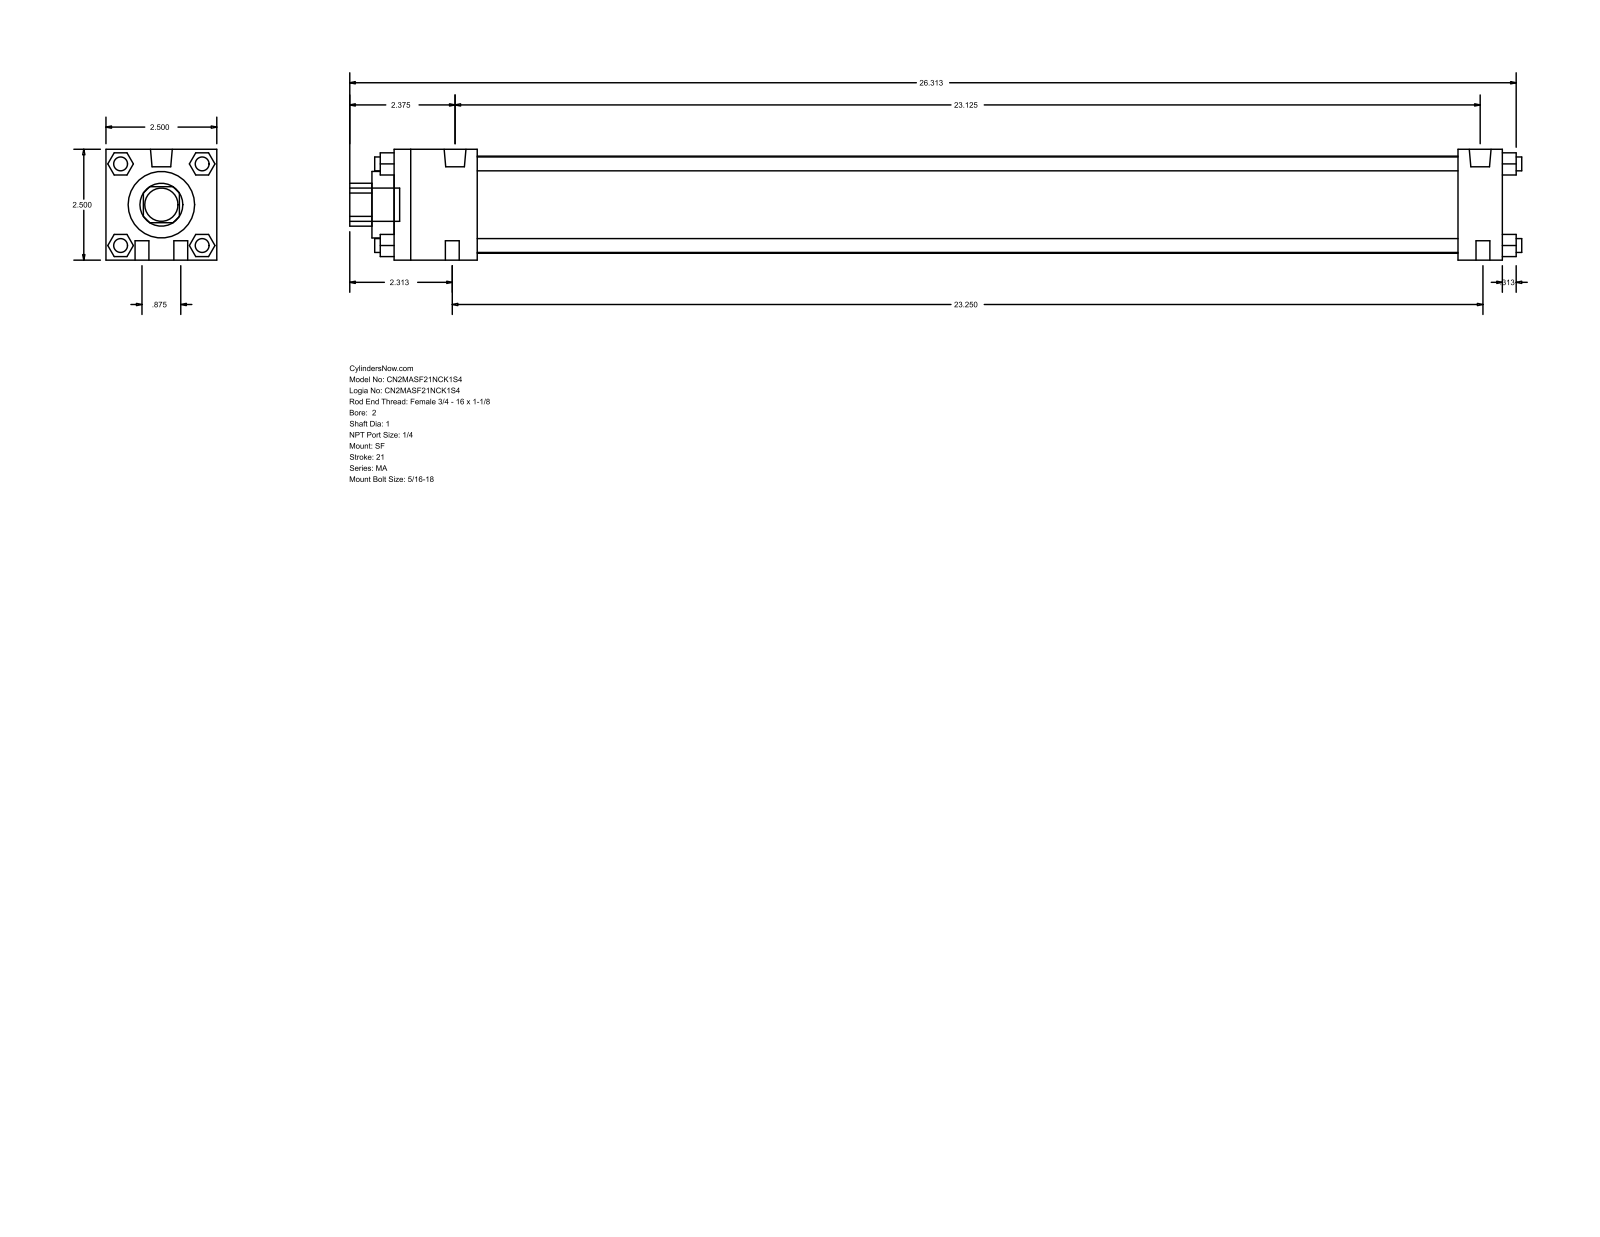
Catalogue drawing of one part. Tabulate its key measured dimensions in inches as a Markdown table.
| quantity | value |
| --- | --- |
| part name | MA_SF__0200_1 |
| STEP written by | GSSL Pune (CONFIG_CONTROL_DESIGN) |
| units | inches |
| bodies | 0 solids, 124 faces (94 planar, 30 cylindrical, 0 other) |
| overall size | 26.437 × 2.5 × 2.5 |
| round holes (diameter × count) | 1 × 1, 1.5 × 1, 2.19 × 1 |
| round bosses / shafts (diameter × count) | 0.313 × 10, 0.492 × 2, 0.75 × 1 |
| partial cylindrical surfaces (radius × count) | 0.484 × 1 |
| main face-to-face distances | 2.5, 25, 0.5, 1, 24, 1.875, 22.125, 23.125, 0.92, 1.593 |
